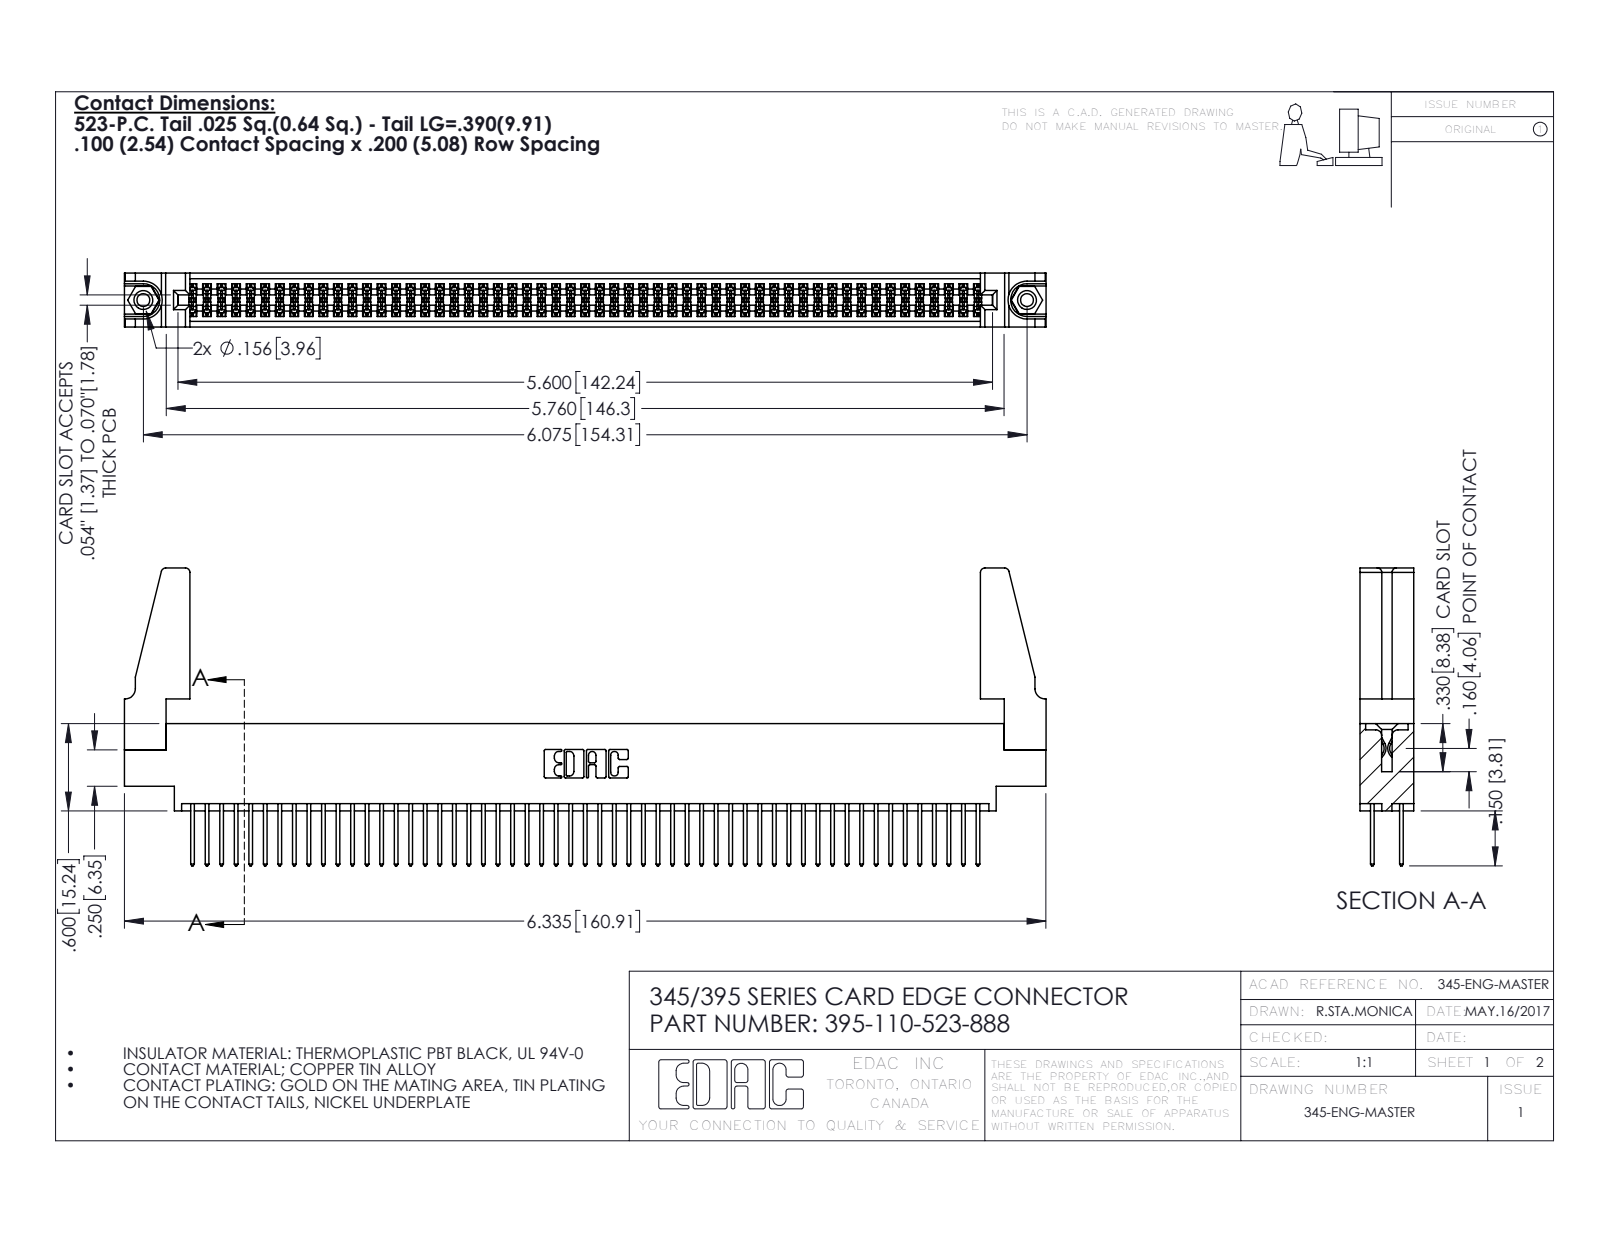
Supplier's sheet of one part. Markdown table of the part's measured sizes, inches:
| quantity | value |
| --- | --- |
| part name | 345-220-078_345-220-088; 345-292-001_345-293-123; 345 Part_0.170 Offset - 0.156 Dia-TH; 395-110-523-888 (+1 more) |
| STEP written by | SolidWorks 2016 (CONFIG_CONTROL_DESIGN) |
| units | inches |
| bodies | 115 solids, 5754 faces (3786 planar, 1952 cylindrical, 16 other) |
| overall size | 6.336 × 2.047 × 0.37 |
| volume | 1.167 in³ |
| surface area | 43.37 in² |
| round holes (diameter × count) | 0.089 × 2, 0.125 × 2, 0.156 × 2, 0.064 × 1 |
| round bosses / shafts (diameter × count) | 0.155 × 2 |
| partial cylindrical surfaces (radius × count) | 0.006 × 165, 0.01 × 110, 0.01 × 22, 0.03 × 8, 0.007 × 6, 0.031 × 6, 0.026 × 3, 0.014 × 2 |
| main face-to-face distances | 0.072, 0.298, 0.37, 0.2, 0.098, 0.272, 0.025, 0.225, 0.175, 0.149 |
| hole center spacings | 0.27, 5.839, 6.075 |
